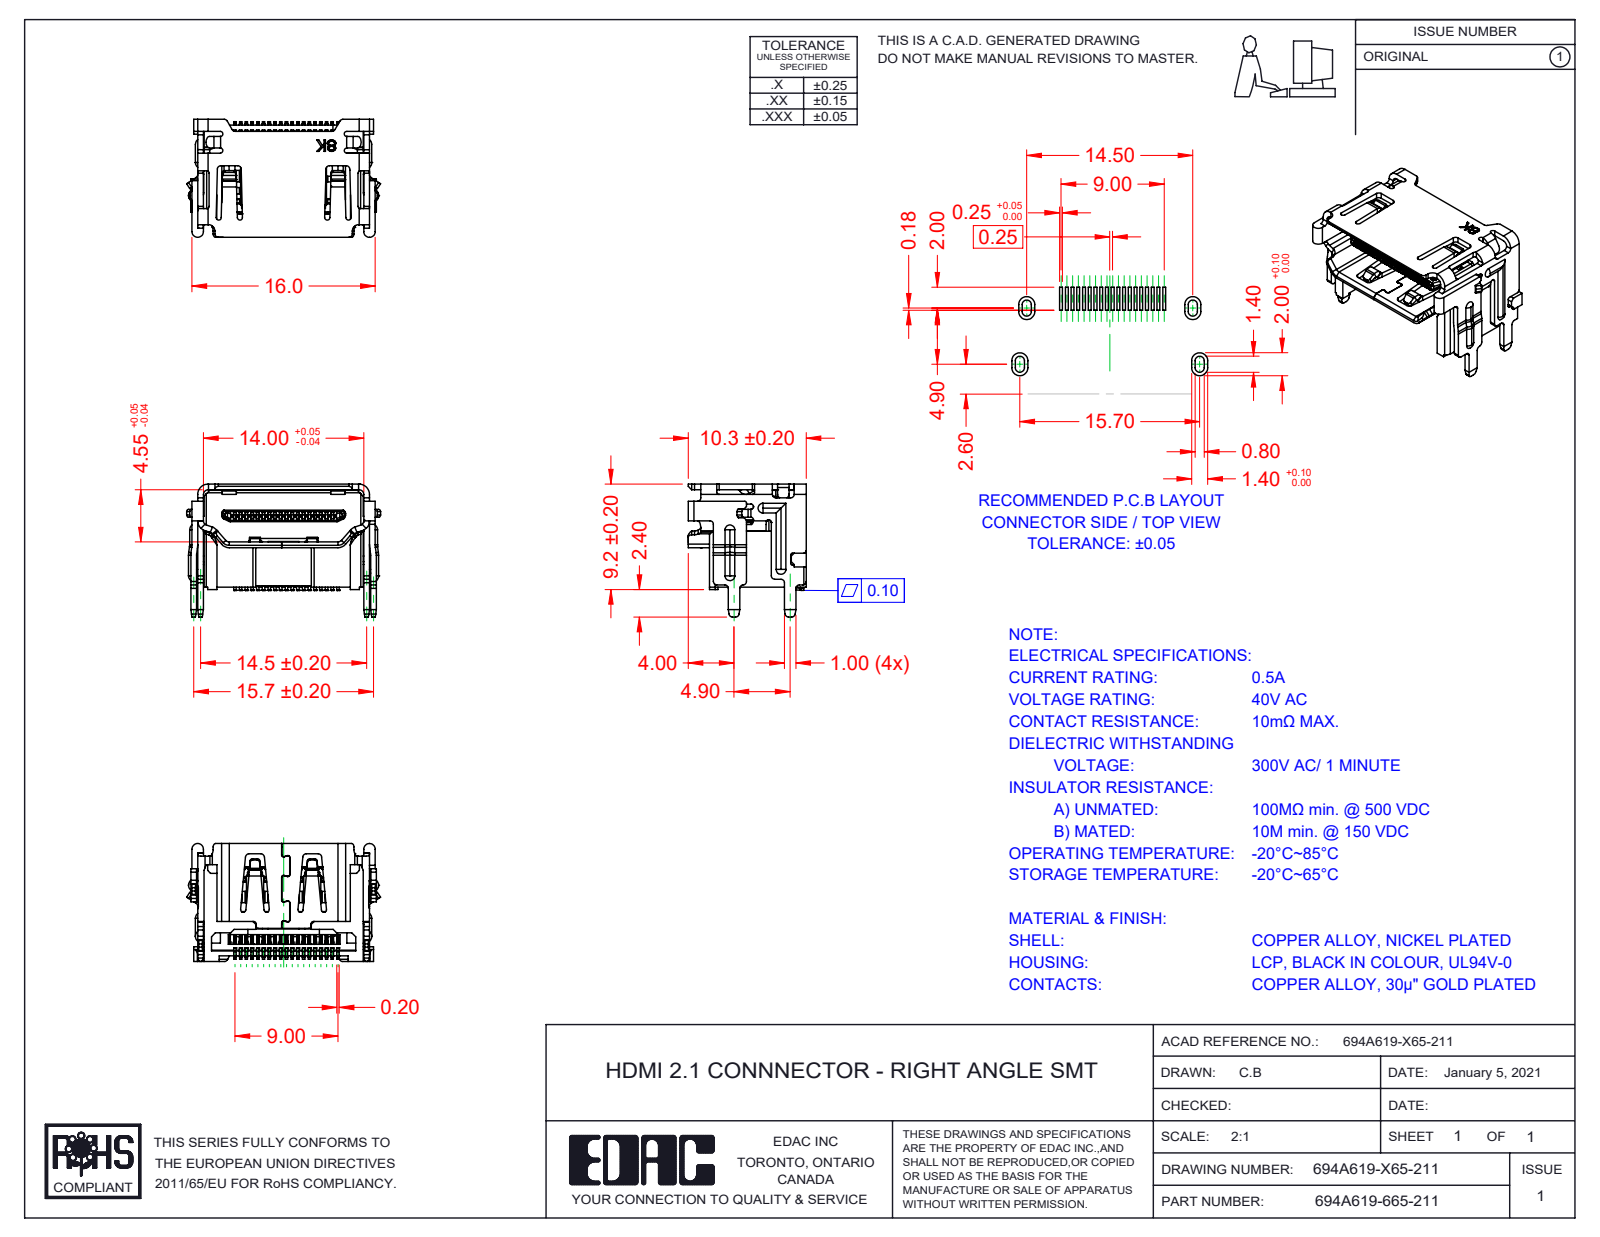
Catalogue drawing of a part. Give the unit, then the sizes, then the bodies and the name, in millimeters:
Units: millimetres
Overall size (bounding box): 16.93 × 11.6 × 10.3
Partial cylindrical surfaces — rounded edges, fillets, slot ends (radius × count): R0.2 ×358, R0.1 ×54, R0.3 ×50, R0.5 ×28, R0.15 ×25, R0.55 ×22, R0.1 ×20, R0.11 ×19
Main face-to-face distances: 0.5, 1, 2.53, 0.55, 3.03, 0.85, 1.15, 2, 0.7, 13.95
Volume: 518 mm³ · Surface area: 2 097 mm²
Bodies: 21 solids, 4232 faces (2728 planar, 1379 cylindrical, 125 other)
Part name (STEP PRODUCT): 694A619-165-211; Contact Lower 694A619-X65-211; Insulator 694A619-X65-211; Contact Upper 694A619-X65-211 (+1 more)
STEP written by: SolidWorks 2020 (AUTOMOTIVE_DESIGN)
